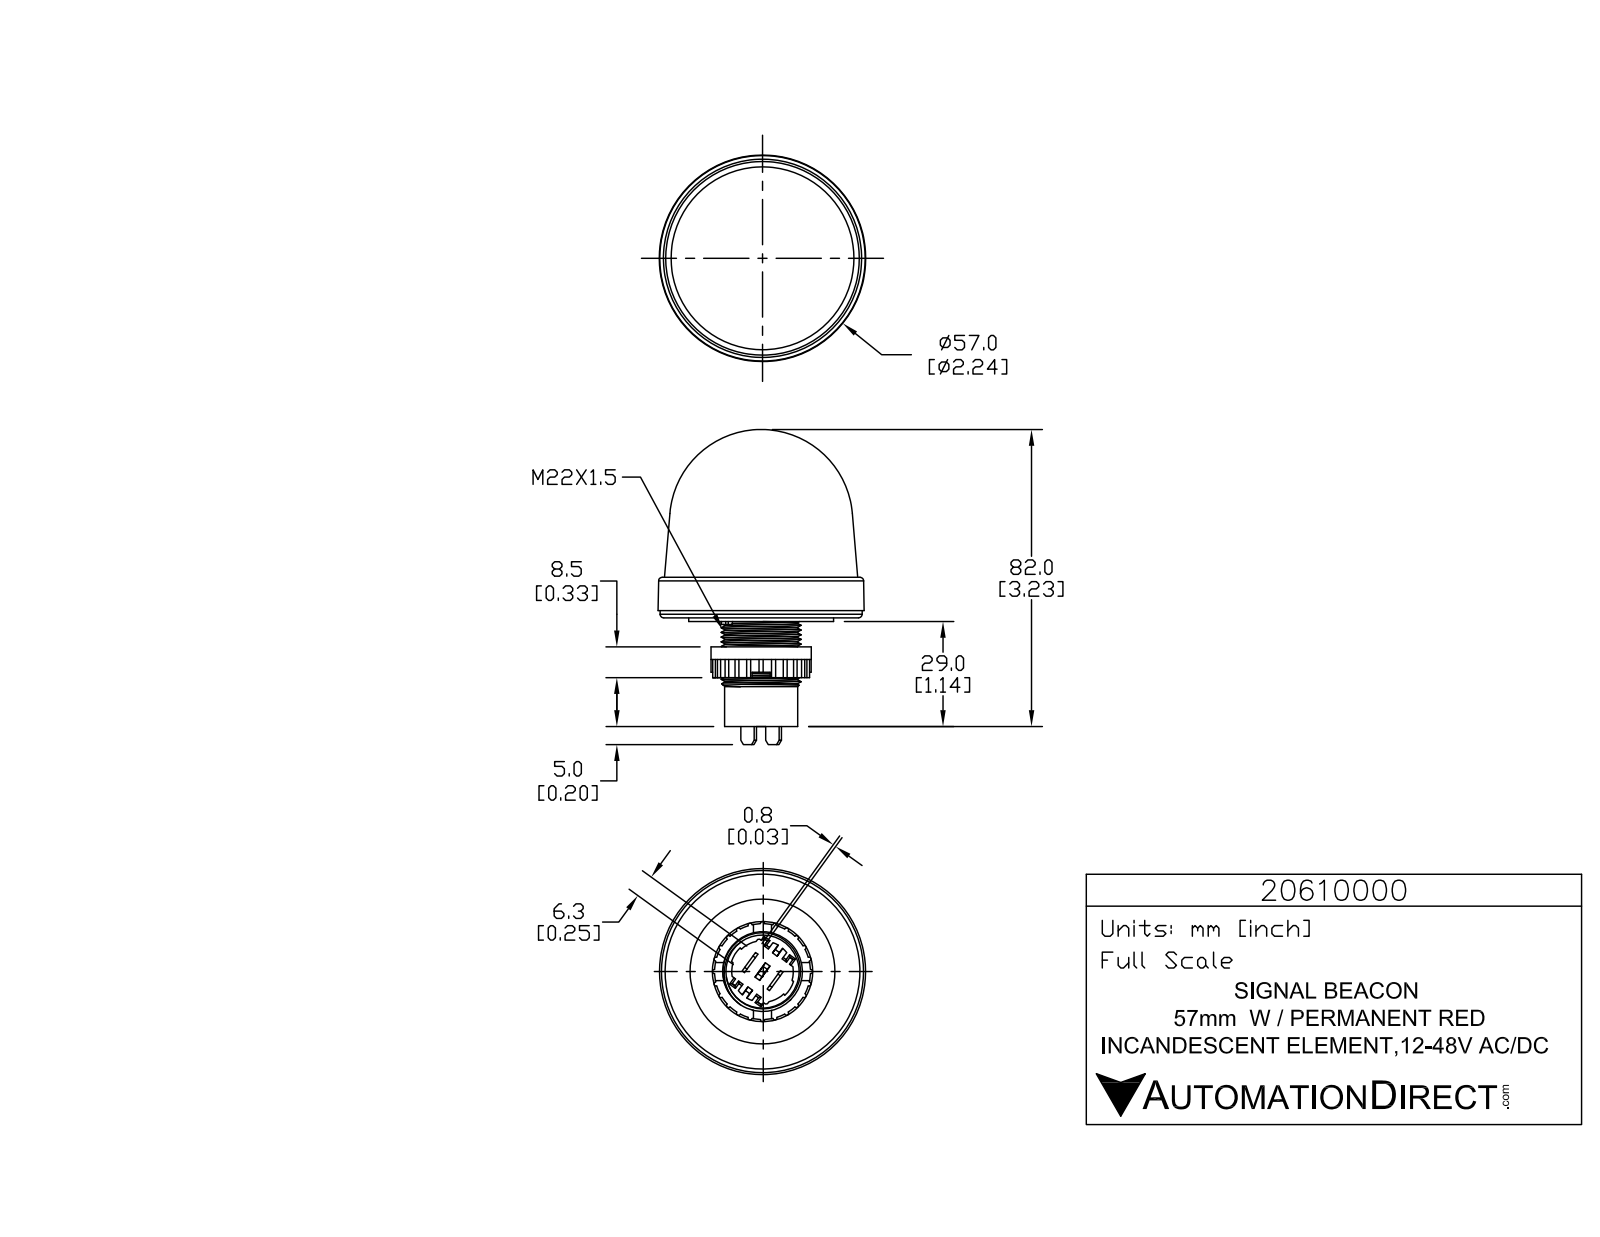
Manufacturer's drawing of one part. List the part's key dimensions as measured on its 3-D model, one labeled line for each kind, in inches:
Part name (STEP PRODUCT): 20610000
STEP written by: SolidWorks 2015 (AUTOMOTIVE_DESIGN)
Units: inches
Bodies: 1 solid, 1002 faces (637 planar, 266 cylindrical, 99 other)
Overall size (bounding box): 3.413 × 2.24 × 2.24
Volume: 6.481 in³ · Surface area: 26.07 in²
Round holes (diameter × count): ⌀0.039 ×3, ⌀0.906 ×1
Round bosses / shafts (diameter × count): ⌀0.226 ×3, ⌀0.056 ×3, ⌀2.197 ×1, ⌀1.575 ×1, ⌀1.091 ×1, ⌀0.866 ×1, ⌀0.795 ×1
Partial cylindrical surfaces — rounded edges, fillets, slot ends (radius × count): R0.023 ×24, R0.008 ×6, R0.008 ×6, R0.008 ×6, R0.131 ×6, R0.004 ×3, R0.005 ×3, R0.008 ×3
Main face-to-face distances: 0.039, 0.276, 0.335, 0.315, 1.063, 0.748, 1.024, 0.118, 1.142, 0.413
